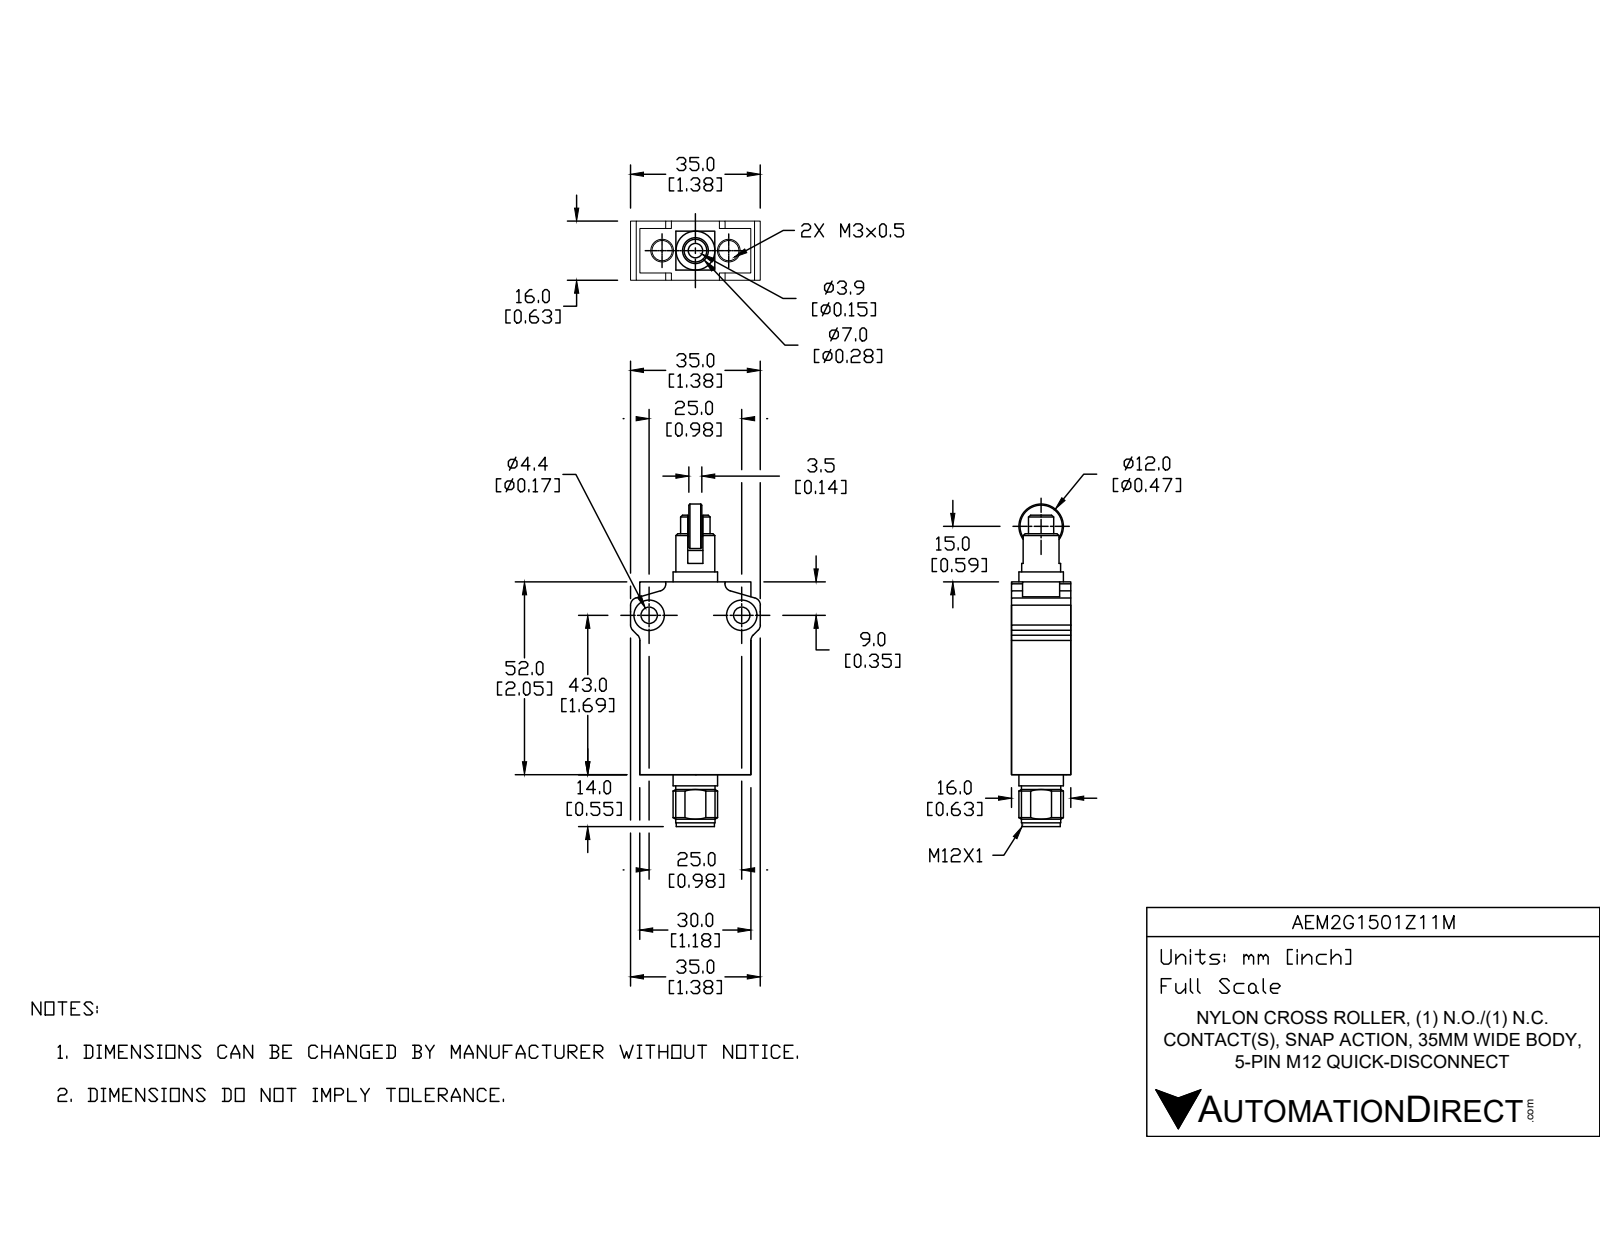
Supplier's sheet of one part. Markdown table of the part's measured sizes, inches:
| quantity | value |
| --- | --- |
| part name | AEM2G1501Z11M |
| STEP written by | SolidWorks 2017 (AUTOMOTIVE_DESIGN) |
| units | inches |
| bodies | 4 solids, 180 faces (67 planar, 72 cylindrical, 41 other) |
| overall size | 3.425 × 1.378 × 0.63 |
| volume | 1.643 in³ |
| surface area | 14.59 in² |
| round holes (diameter × count) | 0.118 × 2, 0.173 × 2, 0.323 × 2, 0.317 × 1 |
| round bosses / shafts (diameter × count) | 0.472 × 2, 0.417 × 1, 0.413 × 1, 0.406 × 1, 0.313 × 1, 0.22 × 1 |
| partial cylindrical surfaces (radius × count) | 0.079 × 8, 0.256 × 1 |
| main face-to-face distances | 0.63, 1.181, 2.047, 0.472, 1.858, 0.189, 0.15, 0.157, 0.51, 0.671 |
| hole center spacings | 0.374, 0.748, 0.984 |
